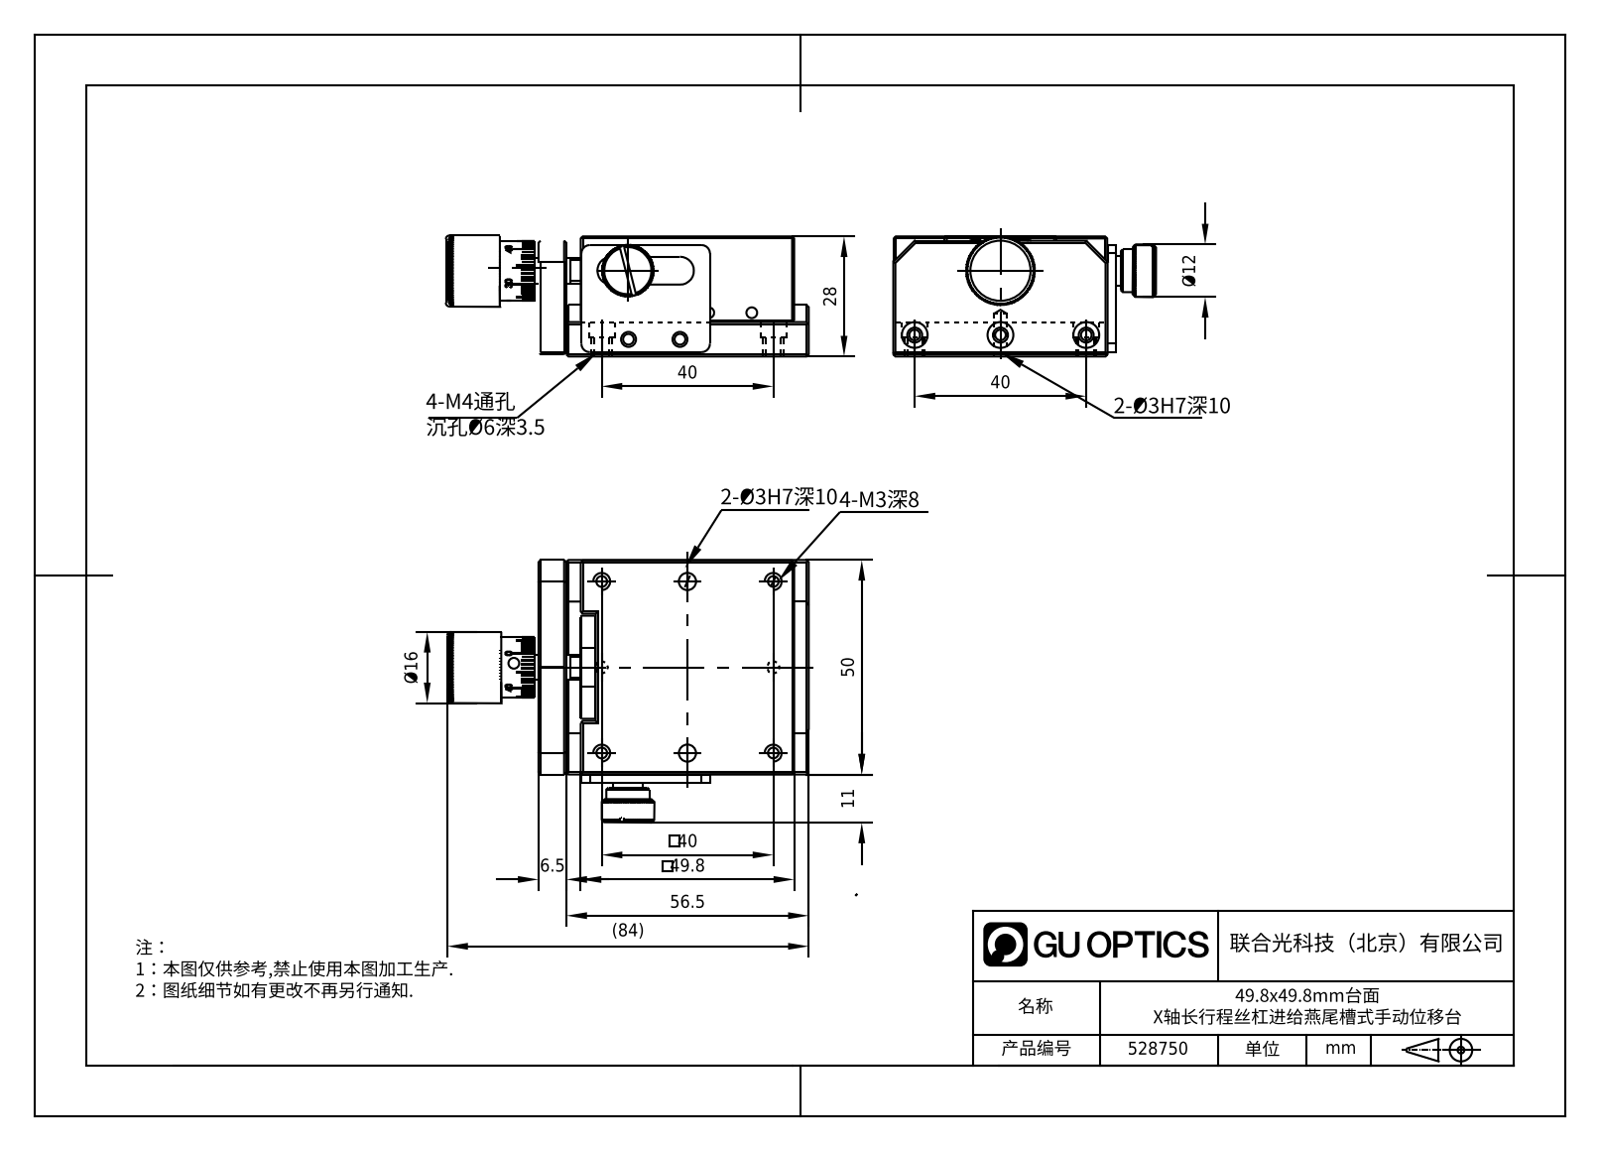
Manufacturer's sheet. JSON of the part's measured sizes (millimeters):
{"part_name": "528750", "step_written_by": "SolidWorks 2020 (CONFIG_CONTROL_DESIGN)", "units": "millimeters", "bodies": {"solids": 0, "faces": 681, "planar": 338, "cylindrical": 167, "other": 176}, "overall_size": [84, 59.45, 28], "round_holes": [[2.5, 12], [2.05, 6], [3.4, 6], [3, 5], [2.9, 4], [5, 4], [6.5, 4], [6, 3], [1.5, 2], [3.1, 2], [3.3, 1], [3.5, 1]], "round_bosses_or_shafts": [[3, 5], [4.5, 4], [2.5, 4], [5.6, 2], [5.5, 2], [13, 1], [12, 1], [10.3, 1]], "partial_cylinders_radius": [[0.3, 8], [2, 4], [2.1, 2], [7.5, 1], [11.5, 1]], "face_to_face_distances": [12, 4.5, 16, 20.5, 27.8, 7.5, 11.8, 7.3, 4.7, 50], "hole_center_spacings": [20, 44.72, 8.5, 40, 28.28, 13.6, 14.72, 15]}
